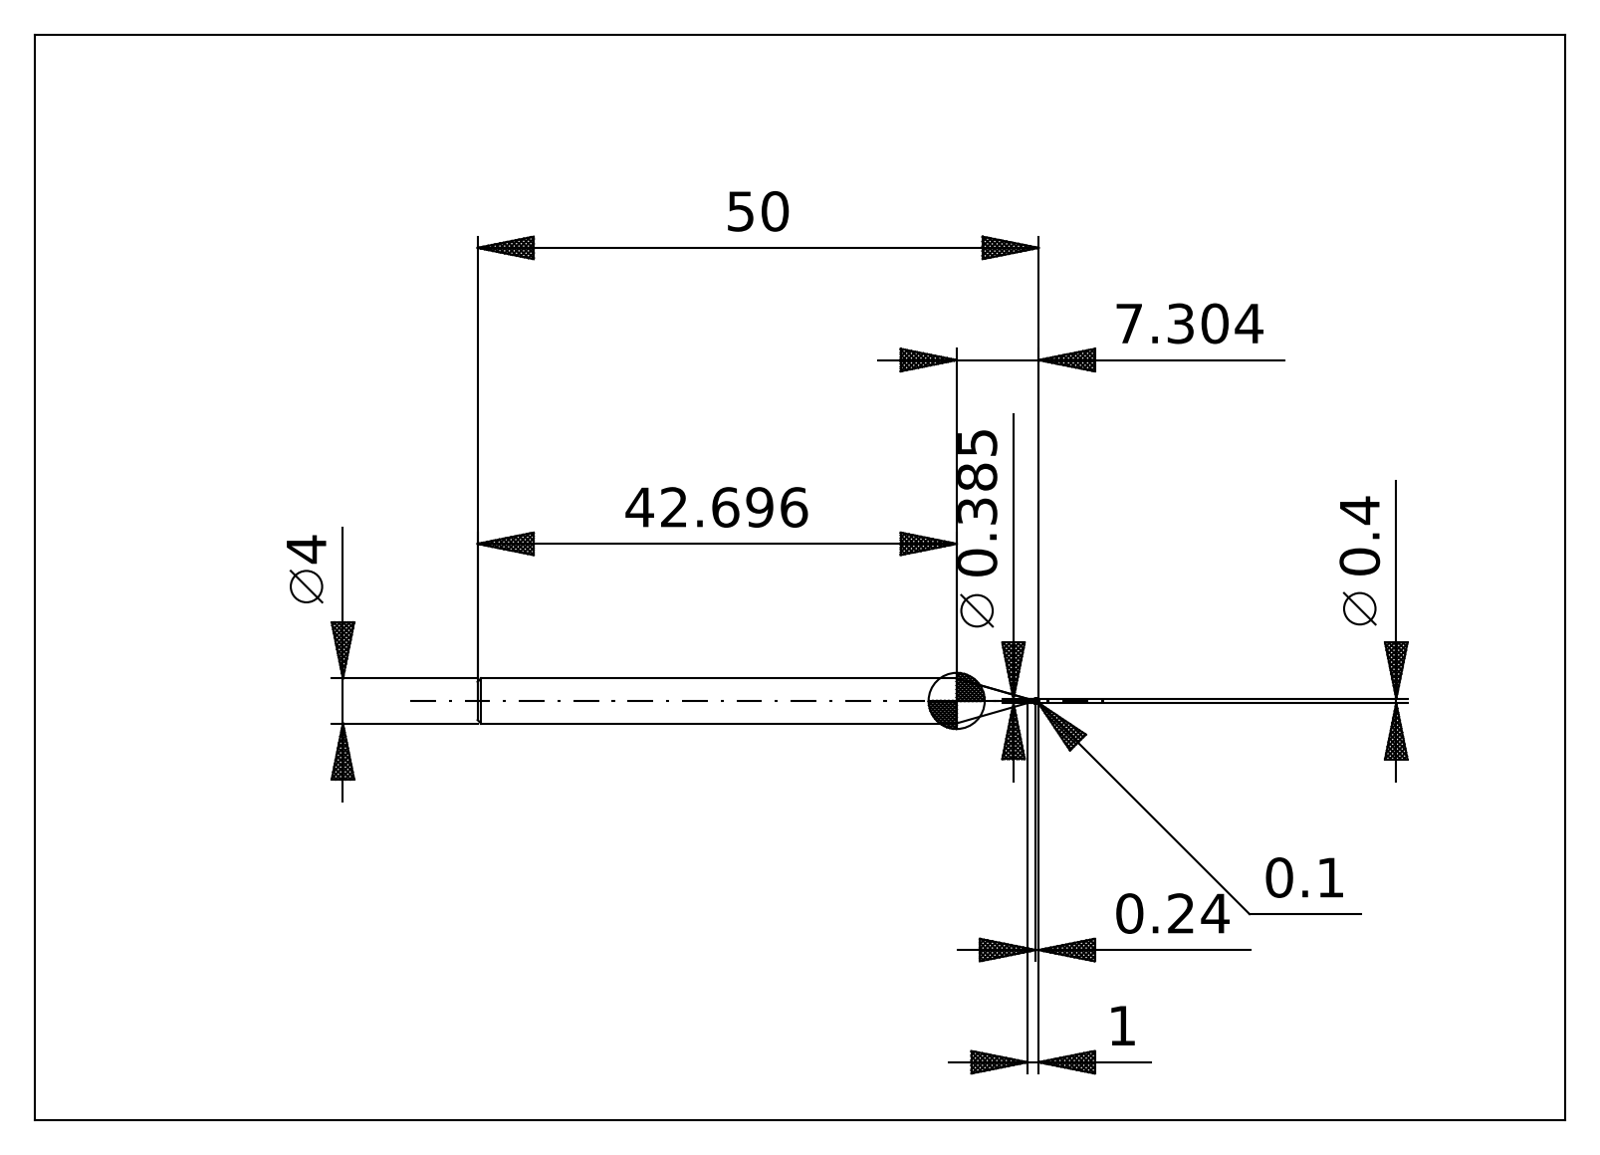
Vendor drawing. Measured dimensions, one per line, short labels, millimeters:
written by: ACIS (automotive_design)
unit: mm
bodies: 2 solids, 26 faces (6 planar, 8 cylindrical, 12 other)
size: 50 × 4 × 4
volume: 565 mm³; area: 594 mm²
bosses: 1× ⌀4, 1× ⌀0.38
face distances: 49.94, 49.76, 50, 7.3, 7.24, 7.06, 42.7
